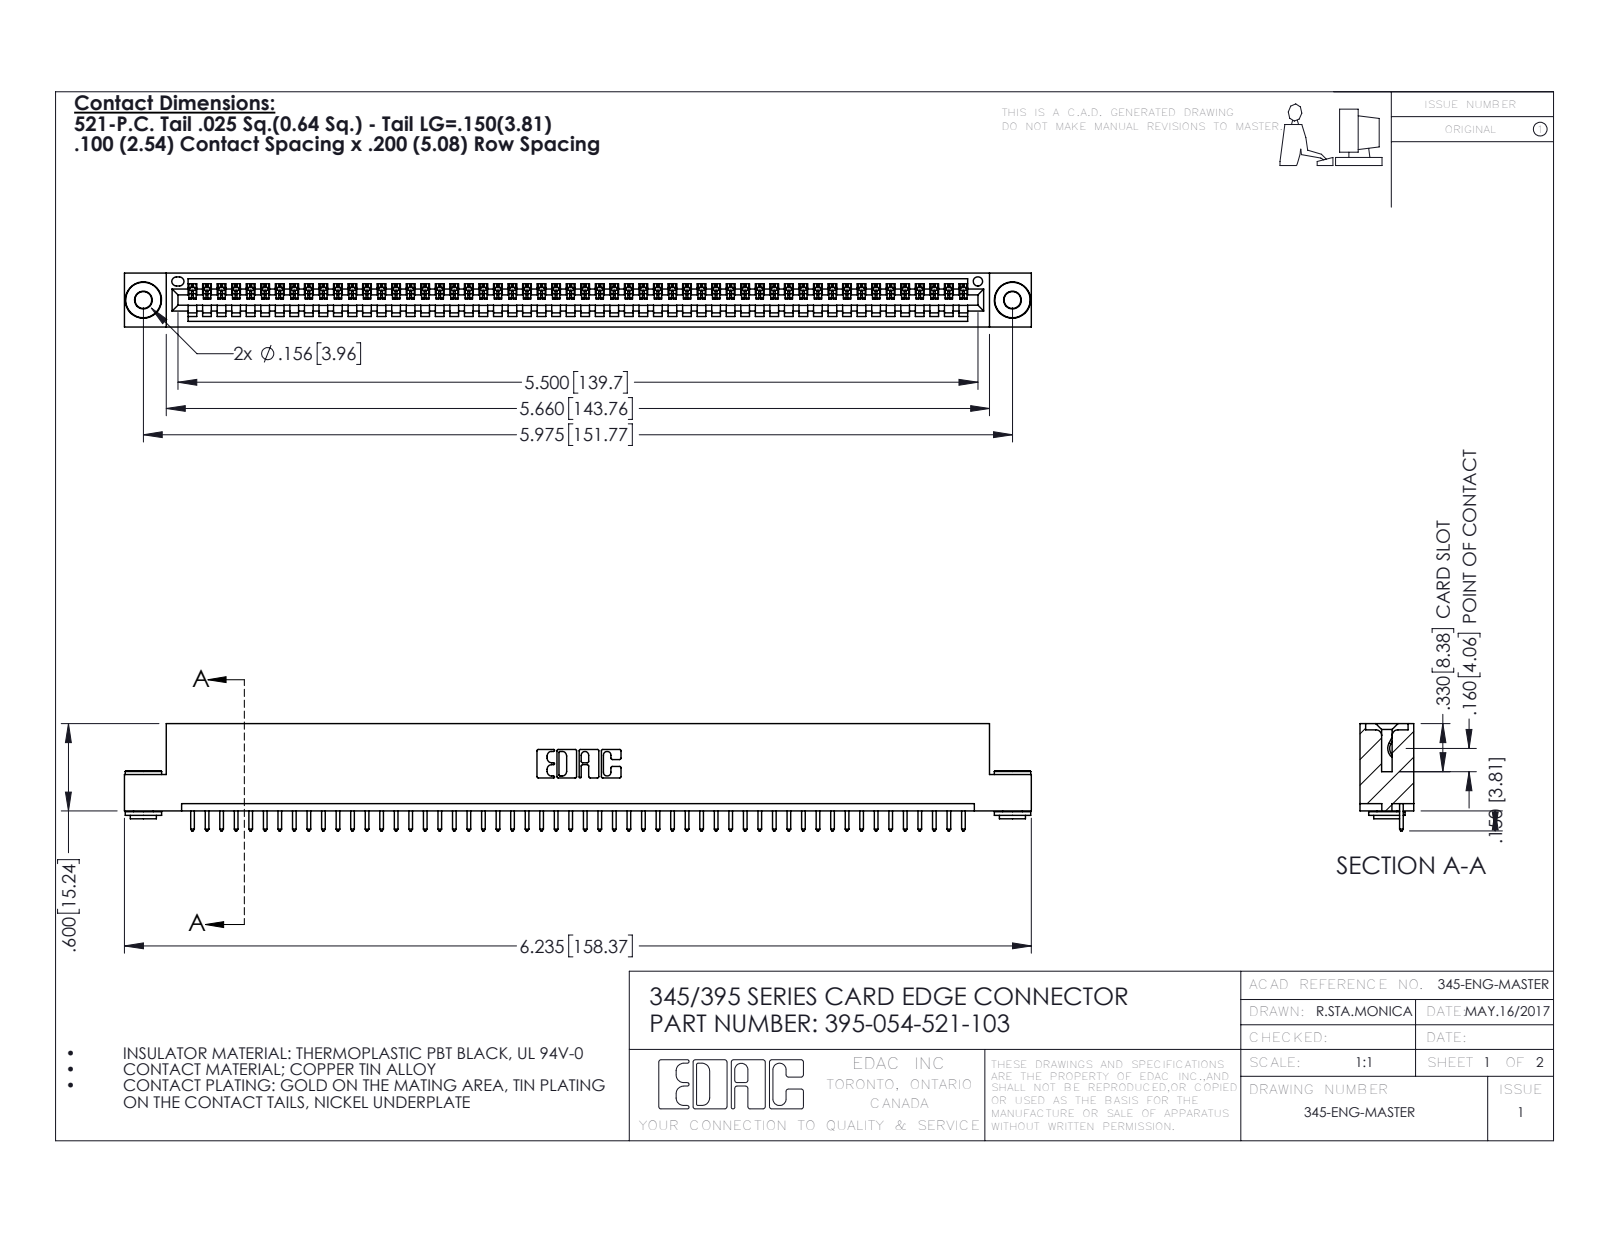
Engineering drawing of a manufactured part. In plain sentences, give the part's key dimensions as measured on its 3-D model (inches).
The part is named "345-250-002_345-250-002-102; 345-292-001_345-293-121; 345 Part_Flush Mounting Lugs - 0.156 Dia-TH; 395-054-521-103". Its 3-D file was written by "SolidWorks 2016 (CONFIG_CONTROL_DESIGN)". It is 57 solids with 3296 faces: 2250 planar, 1038 cylindrical and 8 other. Overall it measures 6.235 by 0.737 by 0.37 inches. Its volume is 0.916 cubic inches and its surface area 30.56 square inches. Round holes: 2 of diameter 0.116, 2 of diameter 0.156, 1 of diameter 0.064. Round bosses or shafts: 2 of diameter 0.25, 2 of diameter 0.18, 2 of diameter 0.136. Partial cylindrical surfaces (rounded edges, fillets, slot ends): 108 of radius 0.006, 108 of radius 0.01, 22 of radius 0.01, 6 of radius 0.007, 6 of radius 0.031, 3 of radius 0.026, 2 of radius 0.031, 2 of radius 0.04. The main face-to-face distances are 0.072, 0.298, 0.37, 0.2, 0.025, 0.098, 0.272, 0.225, 0.149, 0.072. The hole center spacings are 0.27, 5.739, 5.975.
